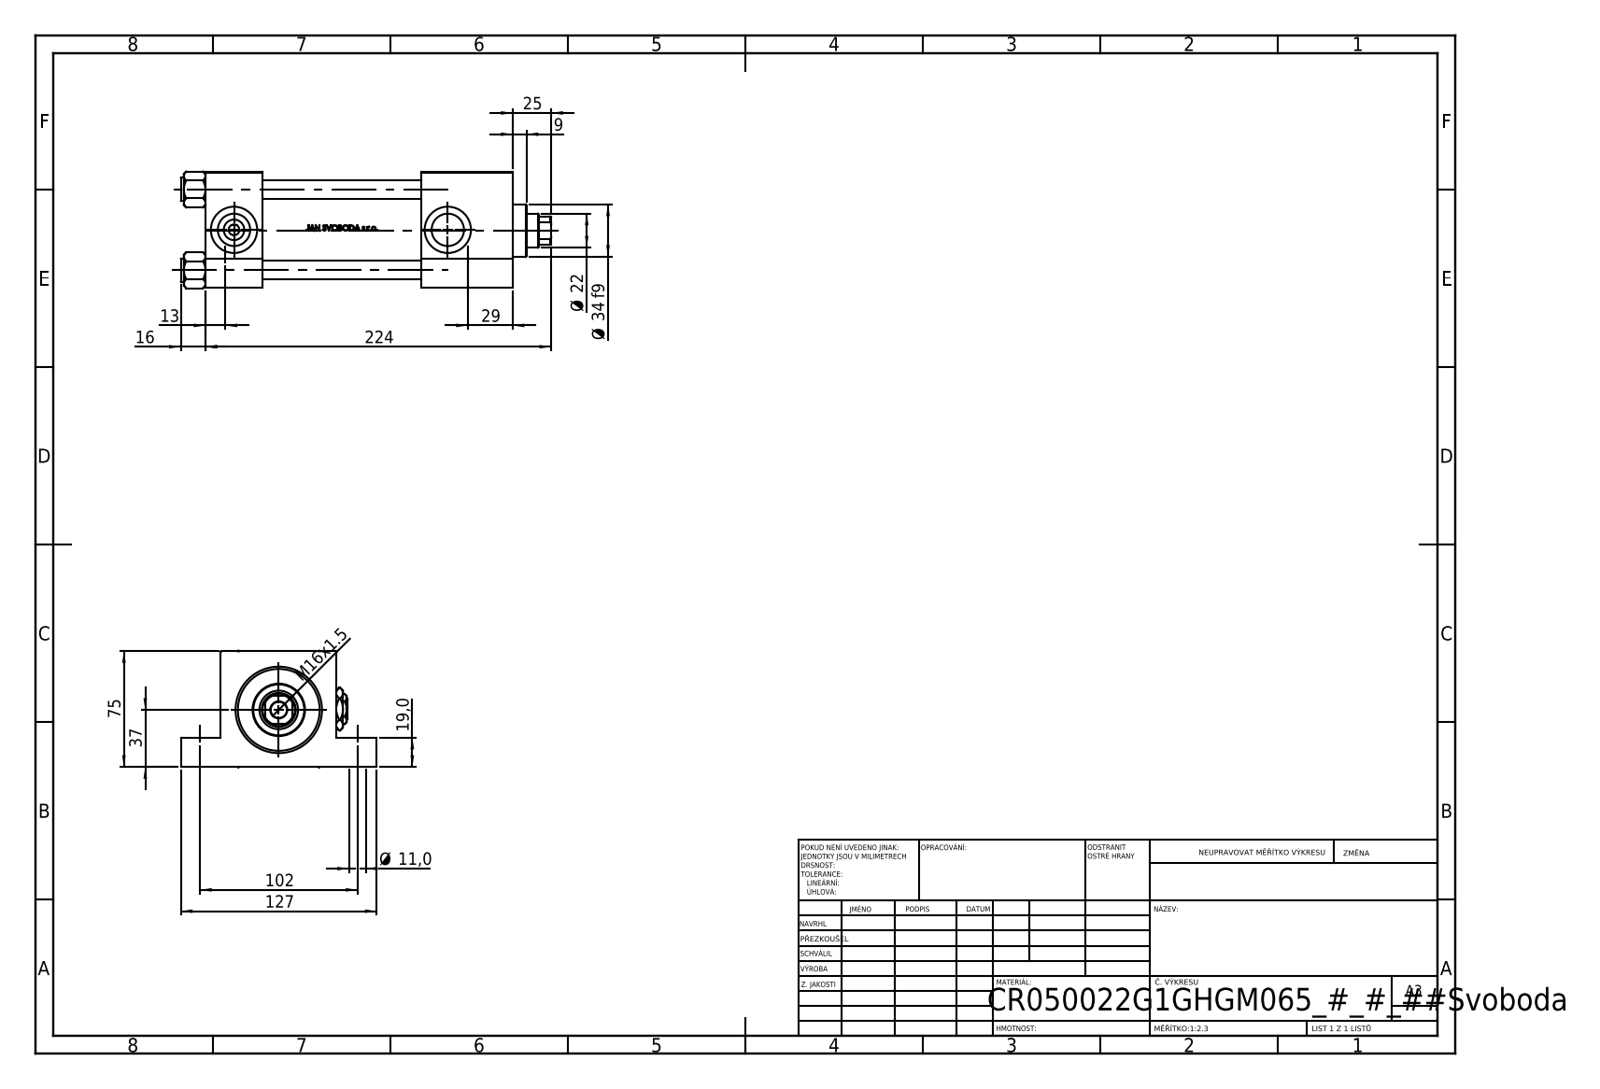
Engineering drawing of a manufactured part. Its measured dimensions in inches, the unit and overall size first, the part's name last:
Units: inches
Overall size (bounding box): 9.449 × 5 × 2.974
Round holes (diameter × count): ⌀0.433 ×4, ⌀0.472 ×4, ⌀0.276 ×2, ⌀0.825 ×2, ⌀1.181 ×2, ⌀0.413 ×1, ⌀0.866 ×1, ⌀0.984 ×1, ⌀1.614 ×1, ⌀1.969 ×1, ⌀2.087 ×1
Round bosses / shafts (diameter × count): ⌀0.591 ×4, ⌀2.205 ×1, ⌀1.339 ×1
Partial cylindrical surfaces — rounded edges, fillets, slot ends (radius × count): R0.413 ×1
Main face-to-face distances: 2.953, 1.457, 7.835, 6.378, 0.748, 2.205, 5.512, 4.055, 2.323, 1.024
Hole centre spacings: 2.059, 1.442, 1.47, 2.912, 4.016, 6.181, 7.371, 5.453
Volume: 49.57 in³ · Surface area: 288.6 in²
Bodies: 12 solids, 1134 faces (454 planar, 128 cylindrical, 552 other)
Part name (STEP PRODUCT): V215_VC_A; V215CR_G_Body; V215CR_VCP_G; NUT_M5_G (+2 more)
STEP written by: SolidWorks 2019 (CONFIG_CONTROL_DESIGN)
